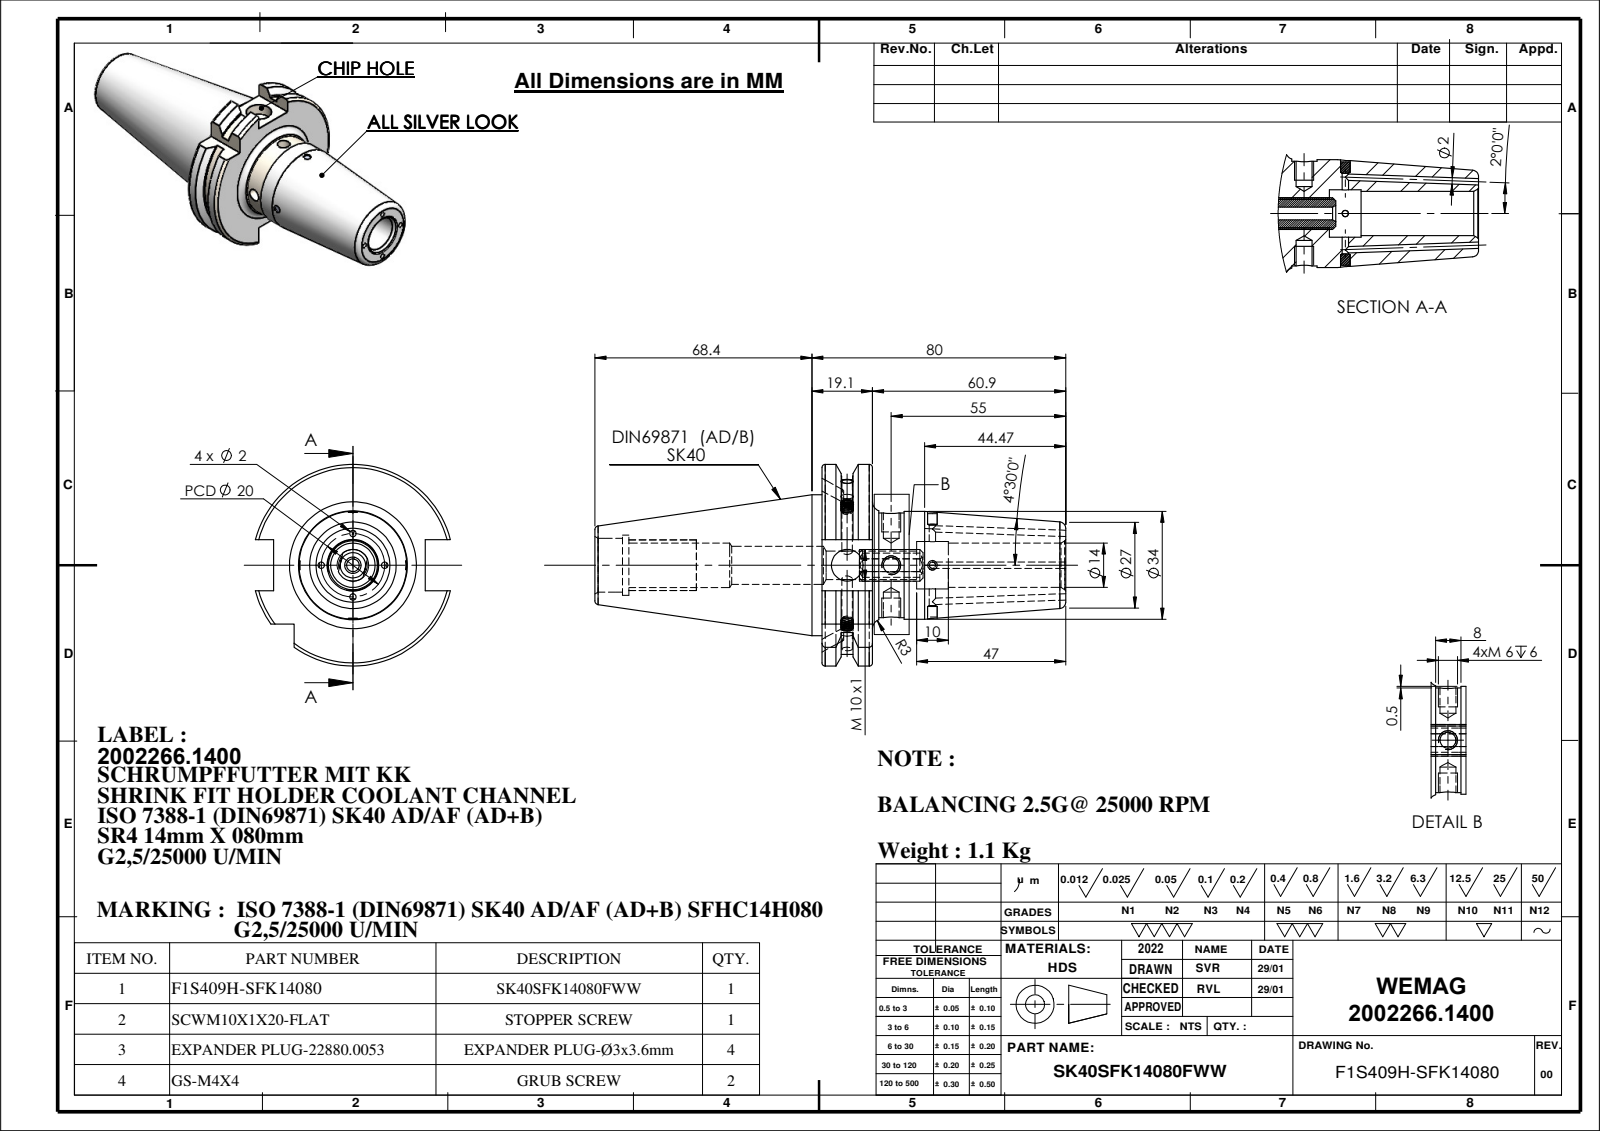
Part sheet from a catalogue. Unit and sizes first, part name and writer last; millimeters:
Units: millimetres
Overall size (bounding box): 148.4 × 63.55 × 61.48
Round holes (diameter × count): ⌀2 ×6, ⌀3 ×2, ⌀5 ×2, ⌀3.3 ×1, ⌀4 ×1, ⌀9 ×1, ⌀10 ×1, ⌀12 ×1, ⌀13.99 ×1, ⌀14 ×1, ⌀14.99 ×1, ⌀17 ×1
Round bosses / shafts (diameter × count): ⌀4 ×2, ⌀44.45 ×1, ⌀34 ×1, ⌀33 ×1
Partial cylindrical surfaces — rounded edges, fillets, slot ends (radius × count): R5 ×1, R28.12 ×1, R31.77 ×1
Main face-to-face distances: 15.9, 60.9, 76.8, 8, 16.1, 47.8, 2, 13.9, 71.6, 87.5
Hole centre spacings: 13, 13.85, 26.85
Volume: 139 687 mm³ · Surface area: 32 230 mm²
Bodies: 8 solids, 301 faces (62 planar, 111 cylindrical, 128 other)
Part name (STEP PRODUCT): SK40SFK14080FWW; GS-M4X4_DIN 913 - M4 x 4-N; SCWM10X1X20-FLAT; 91406-SR414080 (+1 more)
STEP written by: SolidWorks 2018 (CONFIG_CONTROL_DESIGN)
